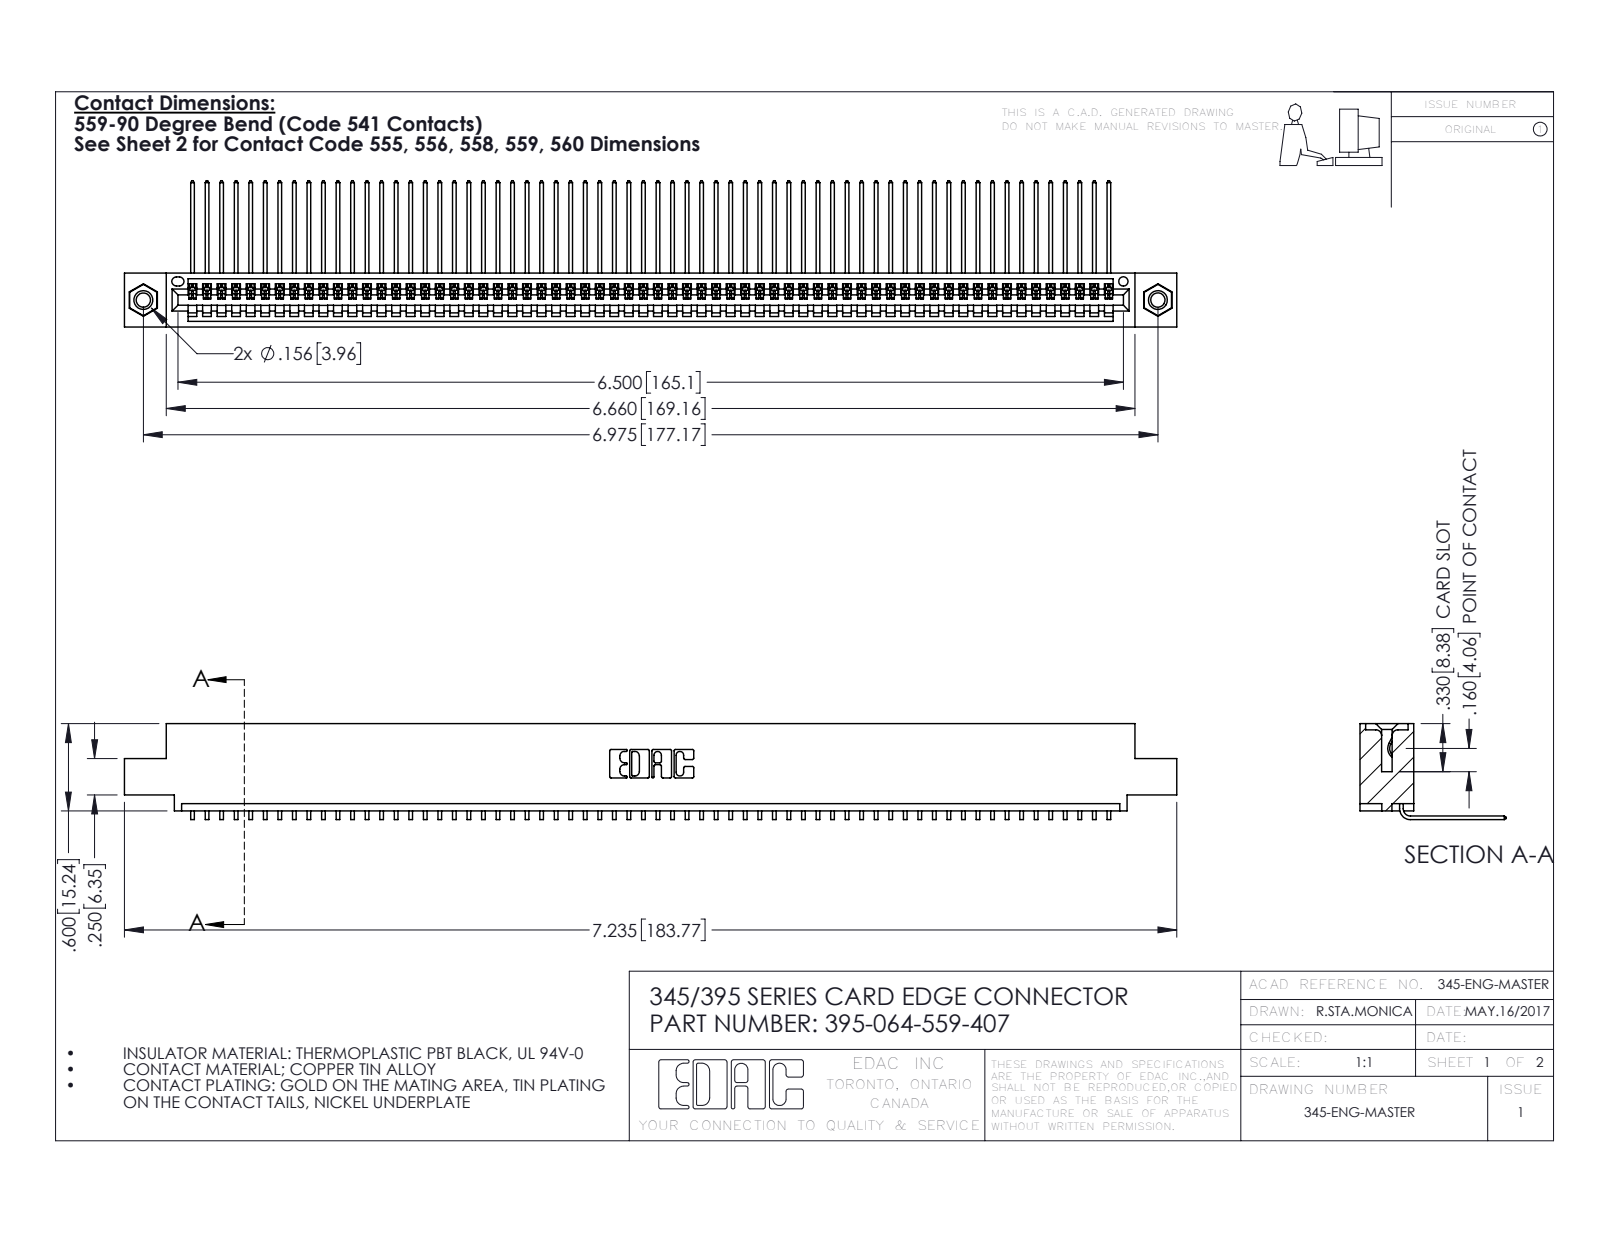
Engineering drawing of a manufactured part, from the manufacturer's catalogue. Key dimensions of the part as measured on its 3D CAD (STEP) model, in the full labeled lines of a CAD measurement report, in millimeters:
Part name (STEP PRODUCT): 345-292-001_558 559 Tail - 1; 345 Part_0.110 Offset - 0.156 Dia-TI; 345-250-001_345-250-005-103; 395-064-559-407
STEP written by: SolidWorks 2016 (CONFIG_CONTROL_DESIGN)
Units: millimetres
Bodies: 67 solids, 4030 faces (2804 planar, 1210 cylindrical, 16 other)
Overall size (bounding box): 183.8 × 25.5 × 16.7
Volume: 17 760 mm³ · Surface area: 25 270 mm²
Round holes (diameter × count): ⌀2.5 ×2, ⌀3.2 ×2, ⌀4 ×2, ⌀1.6 ×1
Round bosses / shafts (diameter × count): ⌀3.9 ×2
Partial cylindrical surfaces — rounded edges, fillets, slot ends (radius × count): R0.2 ×128, R0.3 ×22, R0.2 ×6, R0.8 ×6, R0.7 ×3, R0.8 ×2, R1 ×2, R0.4 ×1
Main face-to-face distances: 1.8, 7.6, 9.4, 5.1, 2.5, 6.9, 0.6, 5.7, 3.8, 1.8
Hole centre spacings: 6.9, 171.2, 177.2
